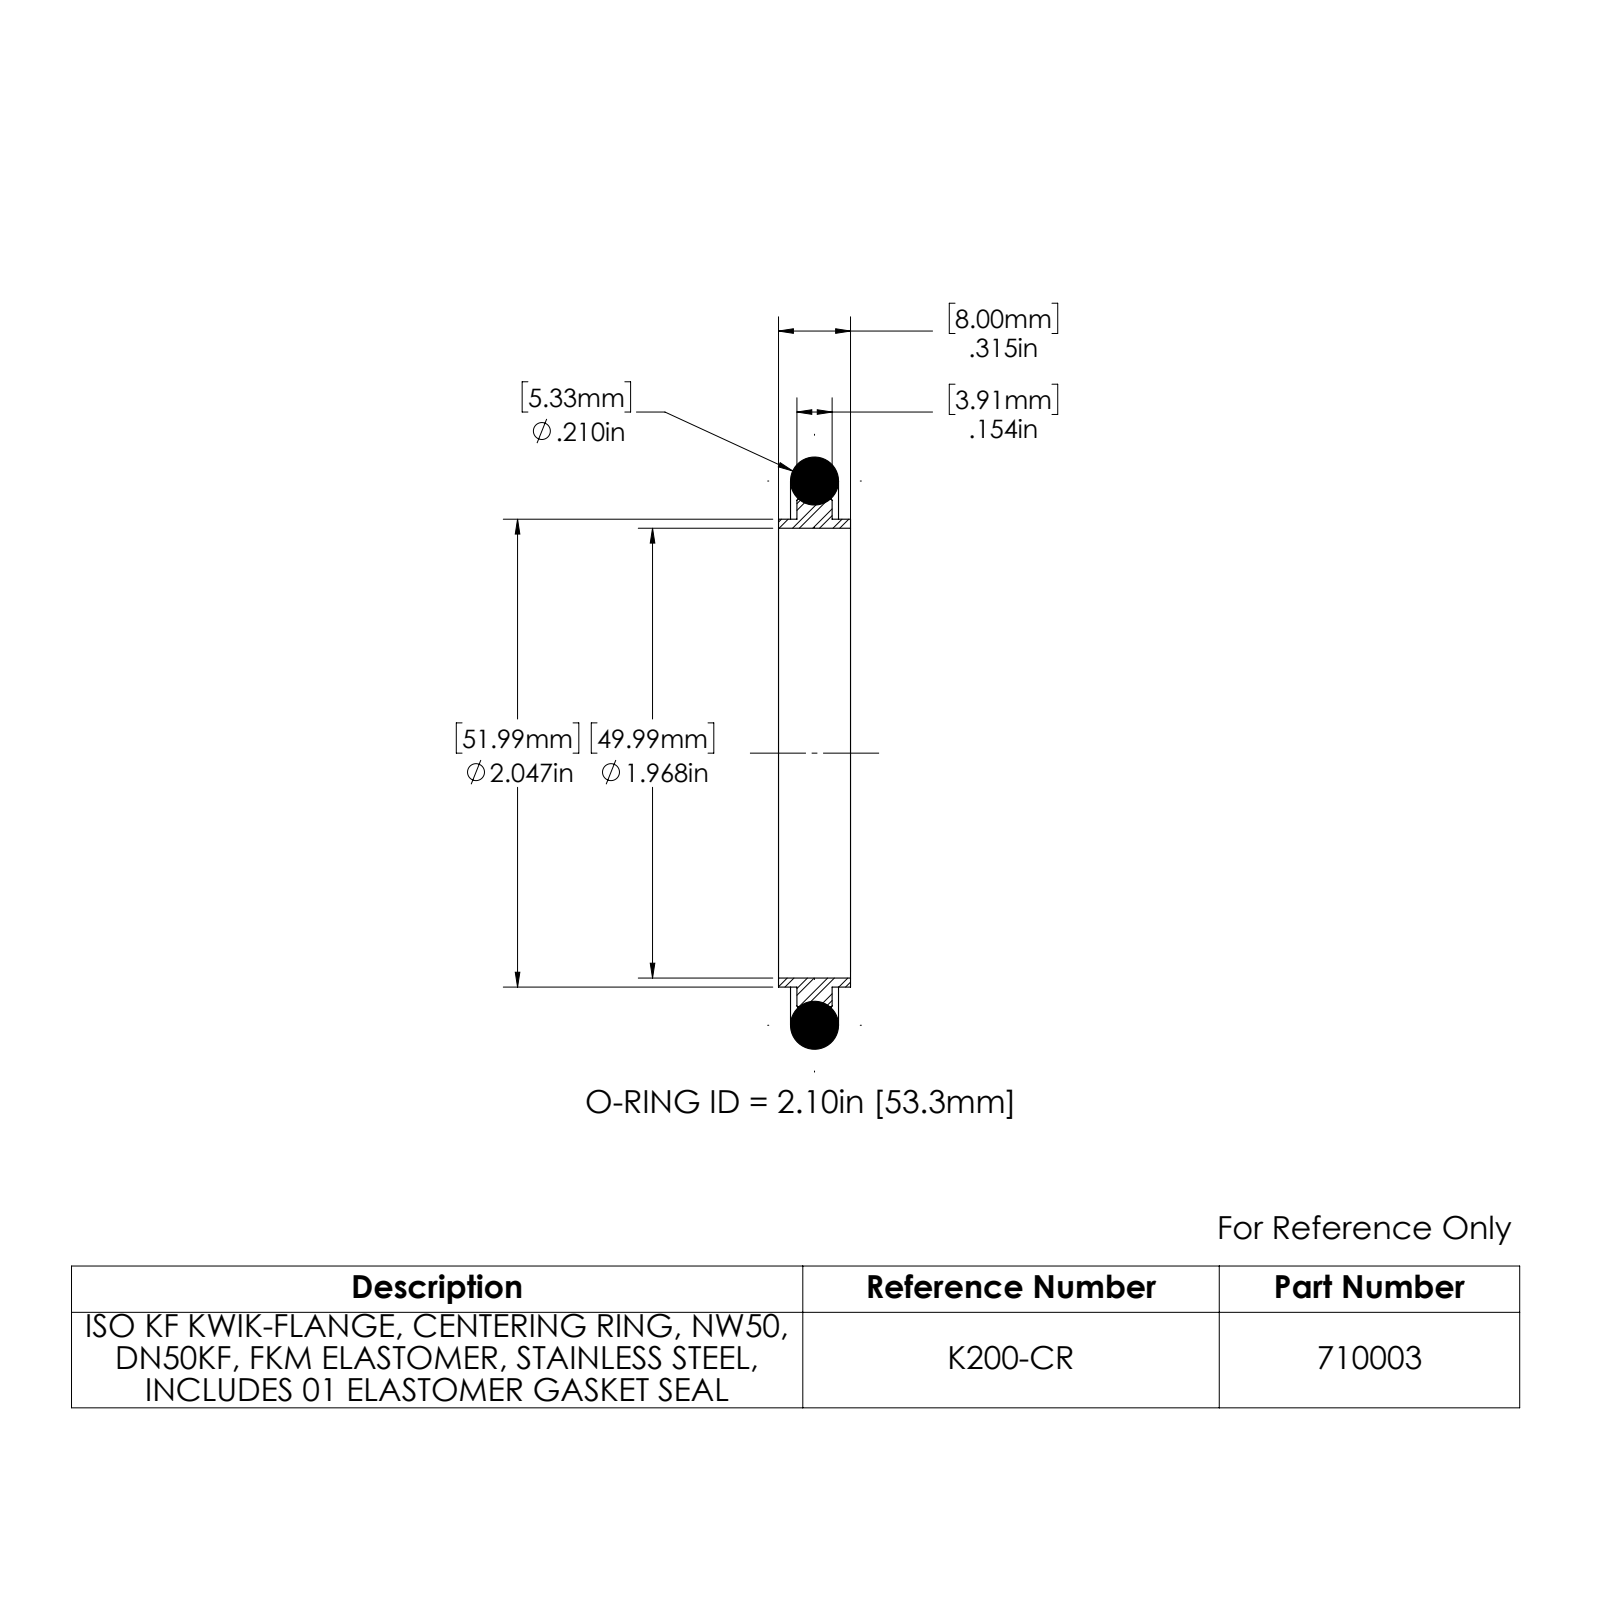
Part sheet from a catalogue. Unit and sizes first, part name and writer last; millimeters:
Units: millimetres
Overall size (bounding box): 65.8 × 65.8 × 8
Round holes (diameter × count): ⌀50 ×1
Round bosses / shafts (diameter × count): ⌀56.4 ×1, ⌀52 ×1
Main face-to-face distances: 3.9, 2, 6, 8
Volume: 6 850 mm³ · Surface area: 6 884 mm²
Bodies: 2 solids, 30 faces (4 planar, 10 cylindrical, 16 other)
Part name (STEP PRODUCT): 710003
STEP written by: SolidWorks 2022 (AUTOMOTIVE_DESIGN)
